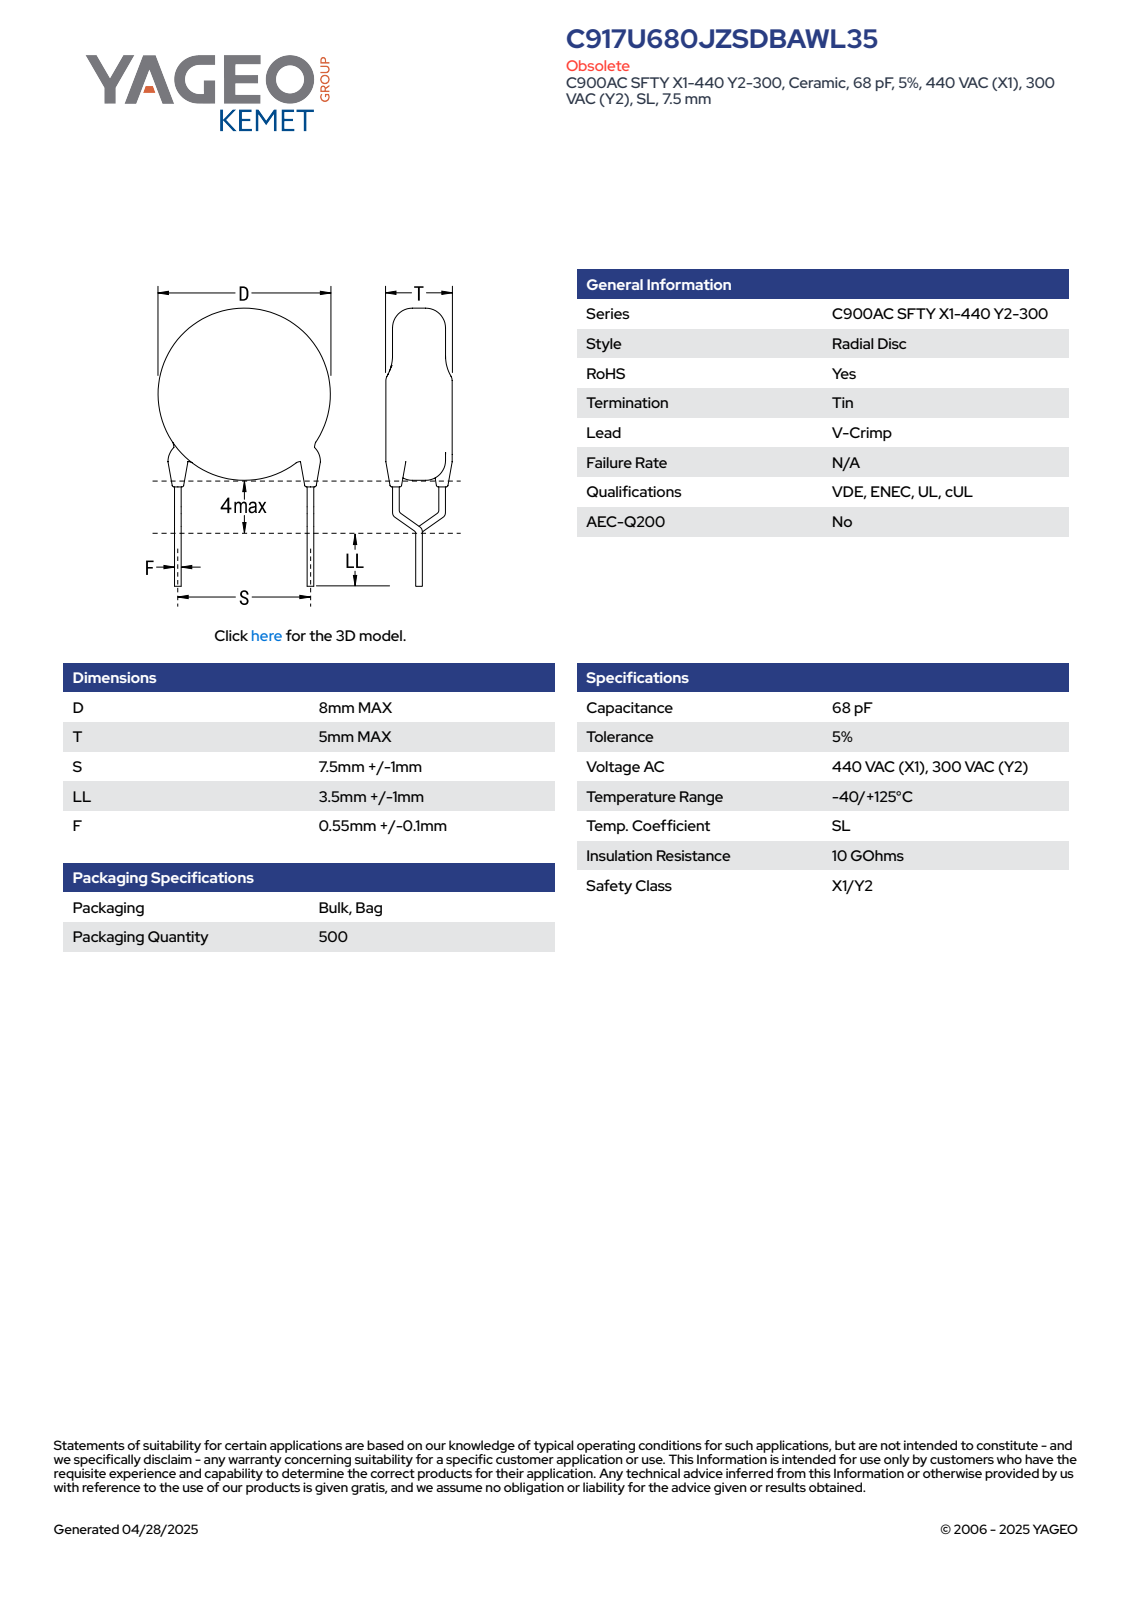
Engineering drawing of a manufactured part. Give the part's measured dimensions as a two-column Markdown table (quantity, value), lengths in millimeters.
| quantity | value |
| --- | --- |
| part name | CCD_VCC900_D8T5S7.5LL4.5F0.65 |
| STEP written by | SolidWorks 2014 (AUTOMOTIVE_DESIGN) |
| units | millimeters |
| bodies | 5 solids, 93 faces (65 planar, 16 cylindrical, 12 other) |
| overall size | 16.3 × 8.15 × 5 |
| volume | 250 mm³ |
| surface area | 255 mm² |
| round bosses / shafts (diameter × count) | 0.65 × 6, 8 × 1 |
| main face-to-face distances | 5, 7.4, 1.04, 12.82, 5.42, 11.78, 4.38, 0.84, 0.45, 0.39 |
